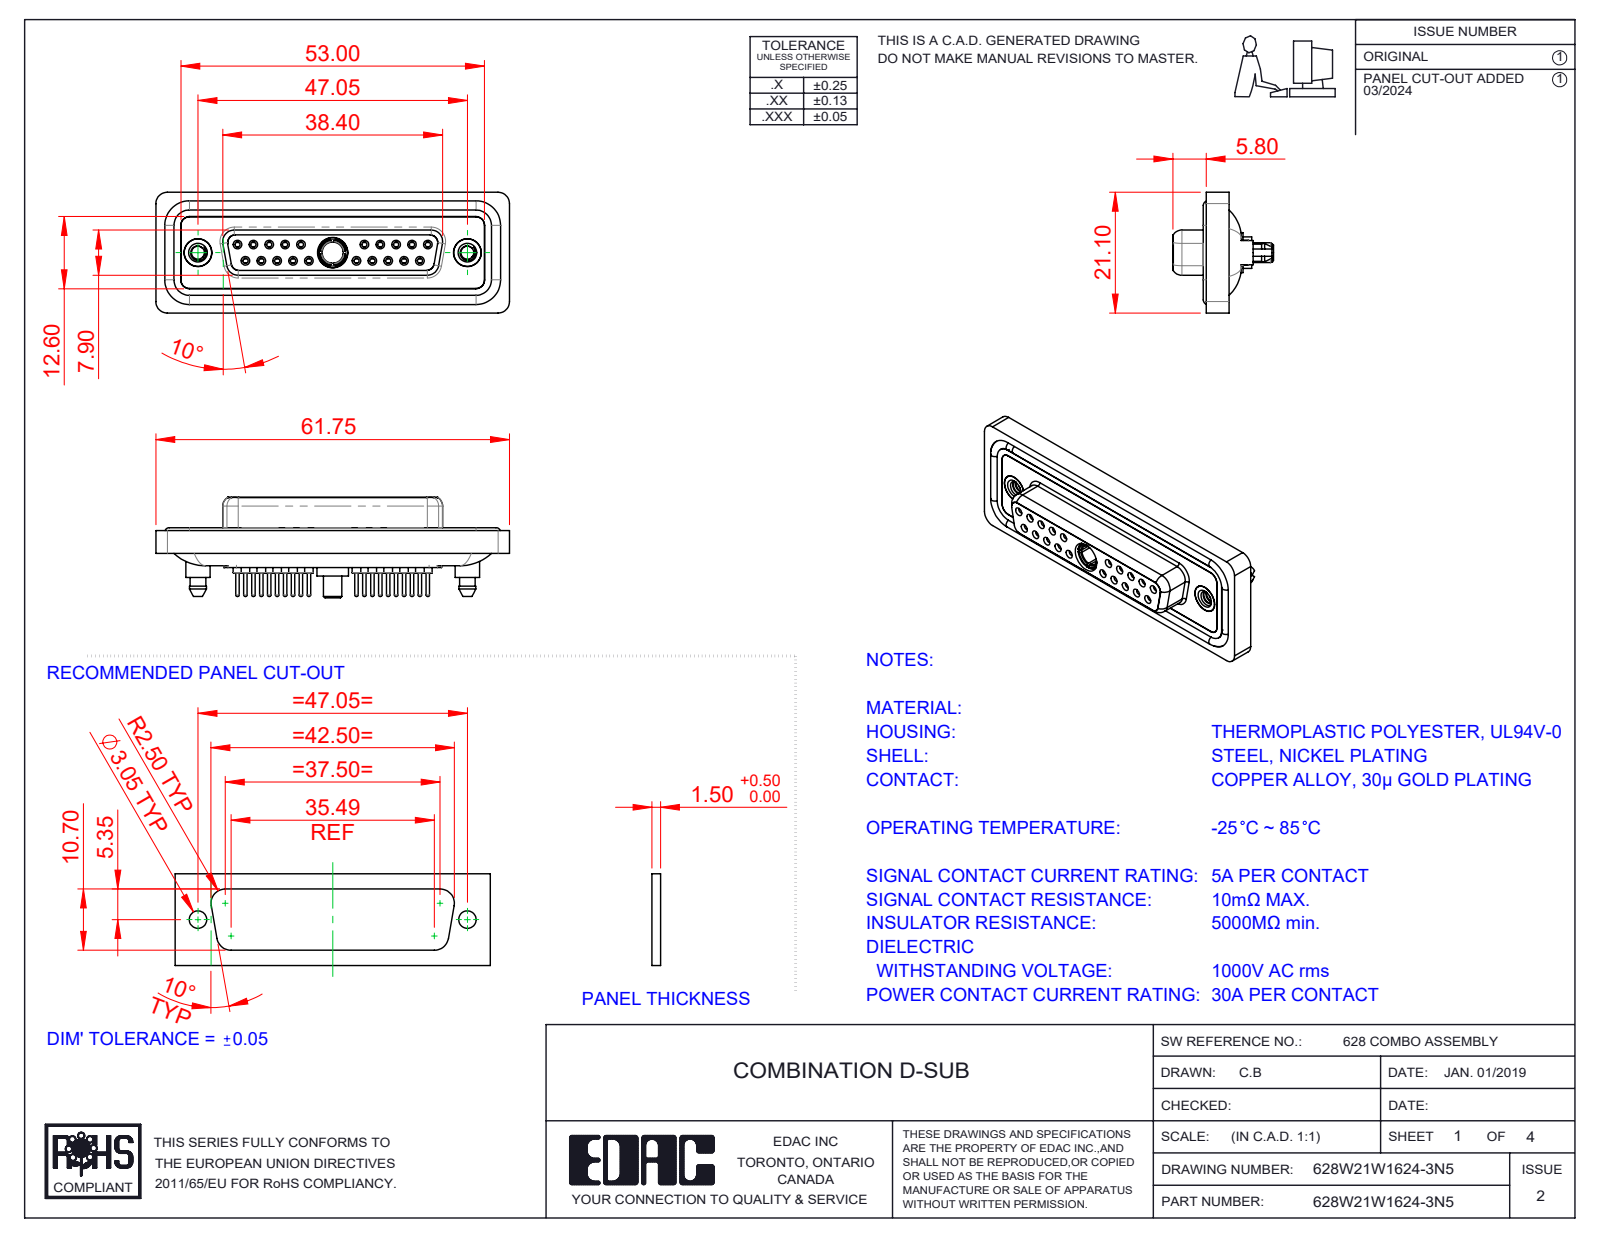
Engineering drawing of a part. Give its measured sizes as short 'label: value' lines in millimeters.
name: 628W21W1624-3N5; 628Combo Shell Rear_25 Contacts; 628Combo Contact Row 2_24; 628Combo Shell Front_25 Contacts (+5 more)
written by: SolidWorks 2023 (CONFIG_CONTROL_DESIGN)
unit: mm
bodies: 29 solids, 1610 faces (450 planar, 623 cylindrical, 537 other)
size: 61.75 × 21.1 × 17.55
volume: 8 515 mm³; area: 14 340 mm²
holes: 20× ⌀0.9, 20× ⌀1.1, 20× ⌀1.5, 20× ⌀2, 10× ⌀1.6, 10× ⌀1.7, 3× ⌀4.85, 2× ⌀2.26, 2× ⌀4, 2× ⌀4.05, 2× ⌀5, 1× ⌀3.7
bosses: 20× ⌀2.2, 20× ⌀0.6, 14× ⌀1.6, 2× ⌀5.4, 2× ⌀4.95, 2× ⌀4.8, 2× ⌀4.25, 1× ⌀5.5
rounds: 24× R1.5, 18× R2, 10× R1.6, 8× R1.35, 4× R0.25, 4× R0.5, 4× R0.6, 4× R0.65
face distances: 0.4, 1.8, 7.45, 6.6, 5.65, 1.6, 0.5, 7.05, 2.9, 1.1
hole spacings: 3.16, 2.77, 5.54, 5.03, 8.31, 7.48, 16.62, 19.39
